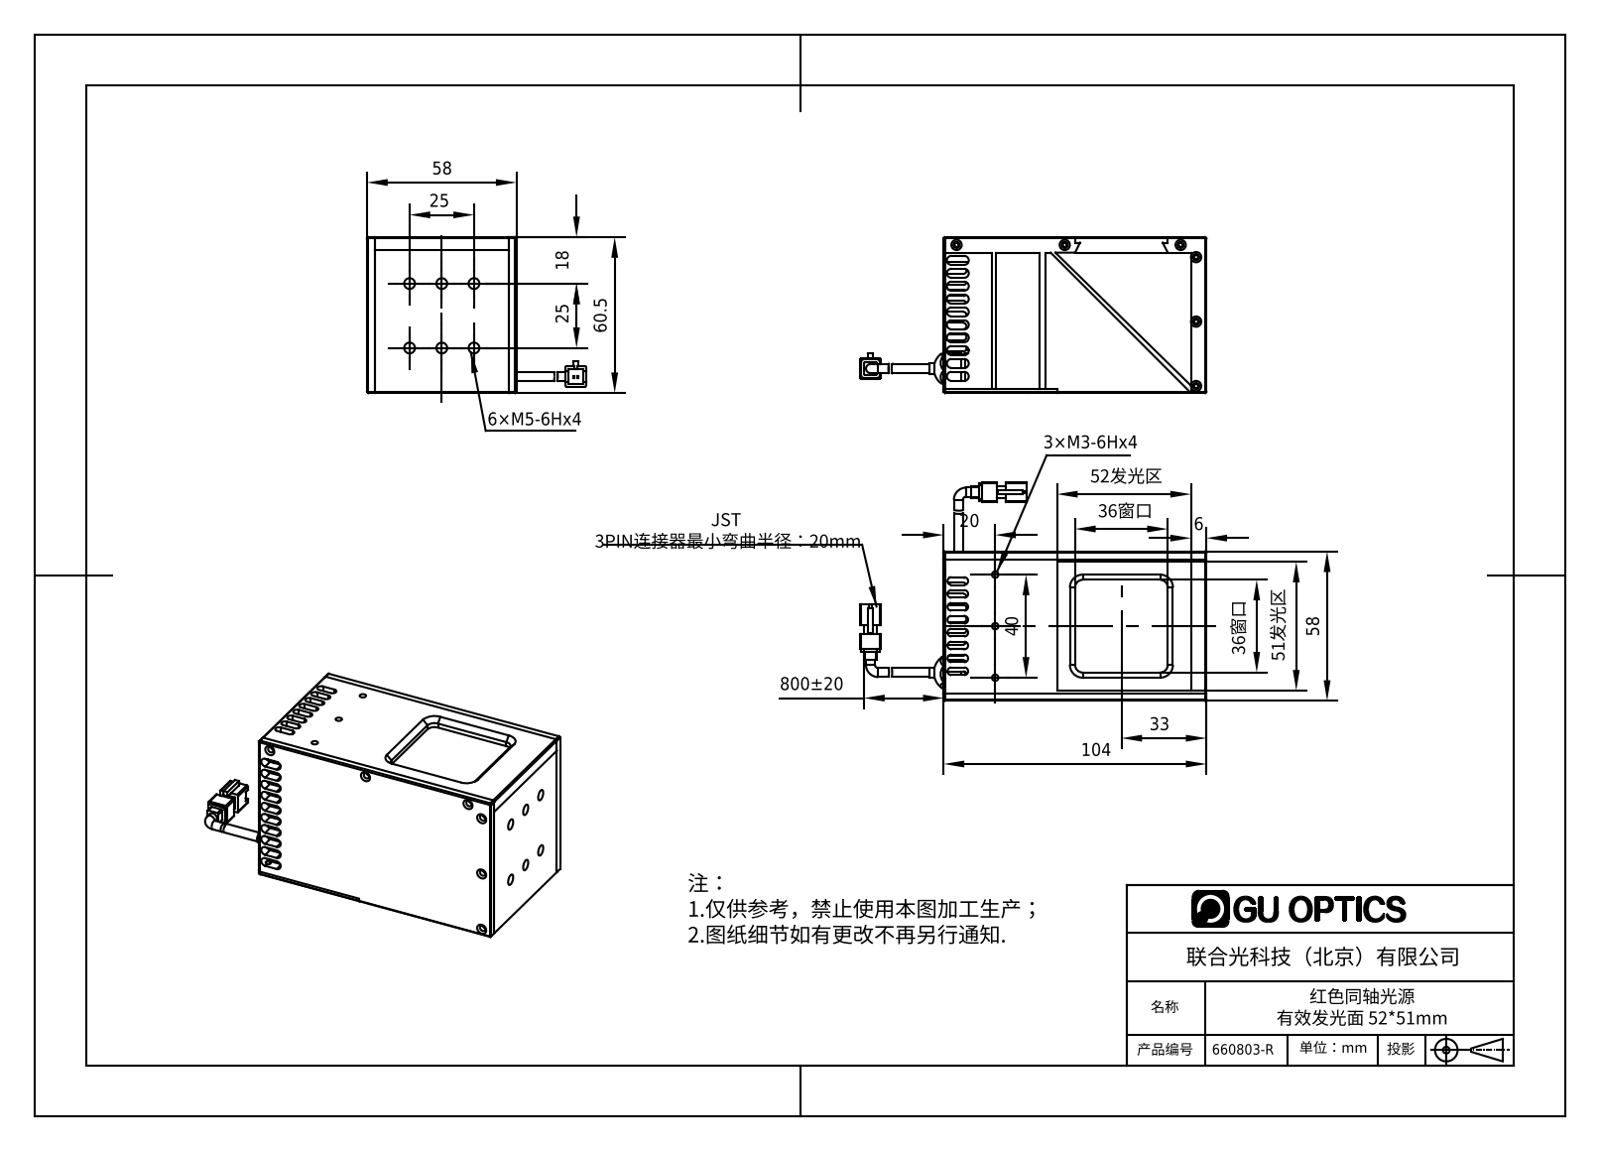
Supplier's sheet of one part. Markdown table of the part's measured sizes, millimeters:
| quantity | value |
| --- | --- |
| part name | 红色同轴光源 有效发光面 5251mm |
| STEP written by | SolidWorks 2016 (AUTOMOTIVE_DESIGN) |
| units | millimeters |
| bodies | 22 solids, 1568 faces (921 planar, 491 cylindrical, 156 other) |
| overall size | 134.4 × 60.7 × 58 |
| volume | 118 035 mm³ |
| surface area | 91 224 mm² |
| round holes (diameter × count) | 1.6 × 13, 2 × 10, 2.4 × 10, 4 × 6, 4.2 × 6, 2.2 × 5, 2.5 × 3, 6.8 × 1 |
| round bosses / shafts (diameter × count) | 3.5 × 2, 9.76 × 1, 8 × 1, 4 × 1 |
| partial cylindrical surfaces (radius × count) | 1.25 × 20, 1.75 × 20, 1.5 × 16, 0.5 × 8, 1 × 4, 3 × 4, 4 × 1, 6.25 × 1 |
| main face-to-face distances | 4, 54, 2, 55, 1, 58, 3, 51, 58.5, 6 |
| hole center spacings | 25, 12.5, 20, 27.95, 30, 3.58, 5.51, 9.03 |
